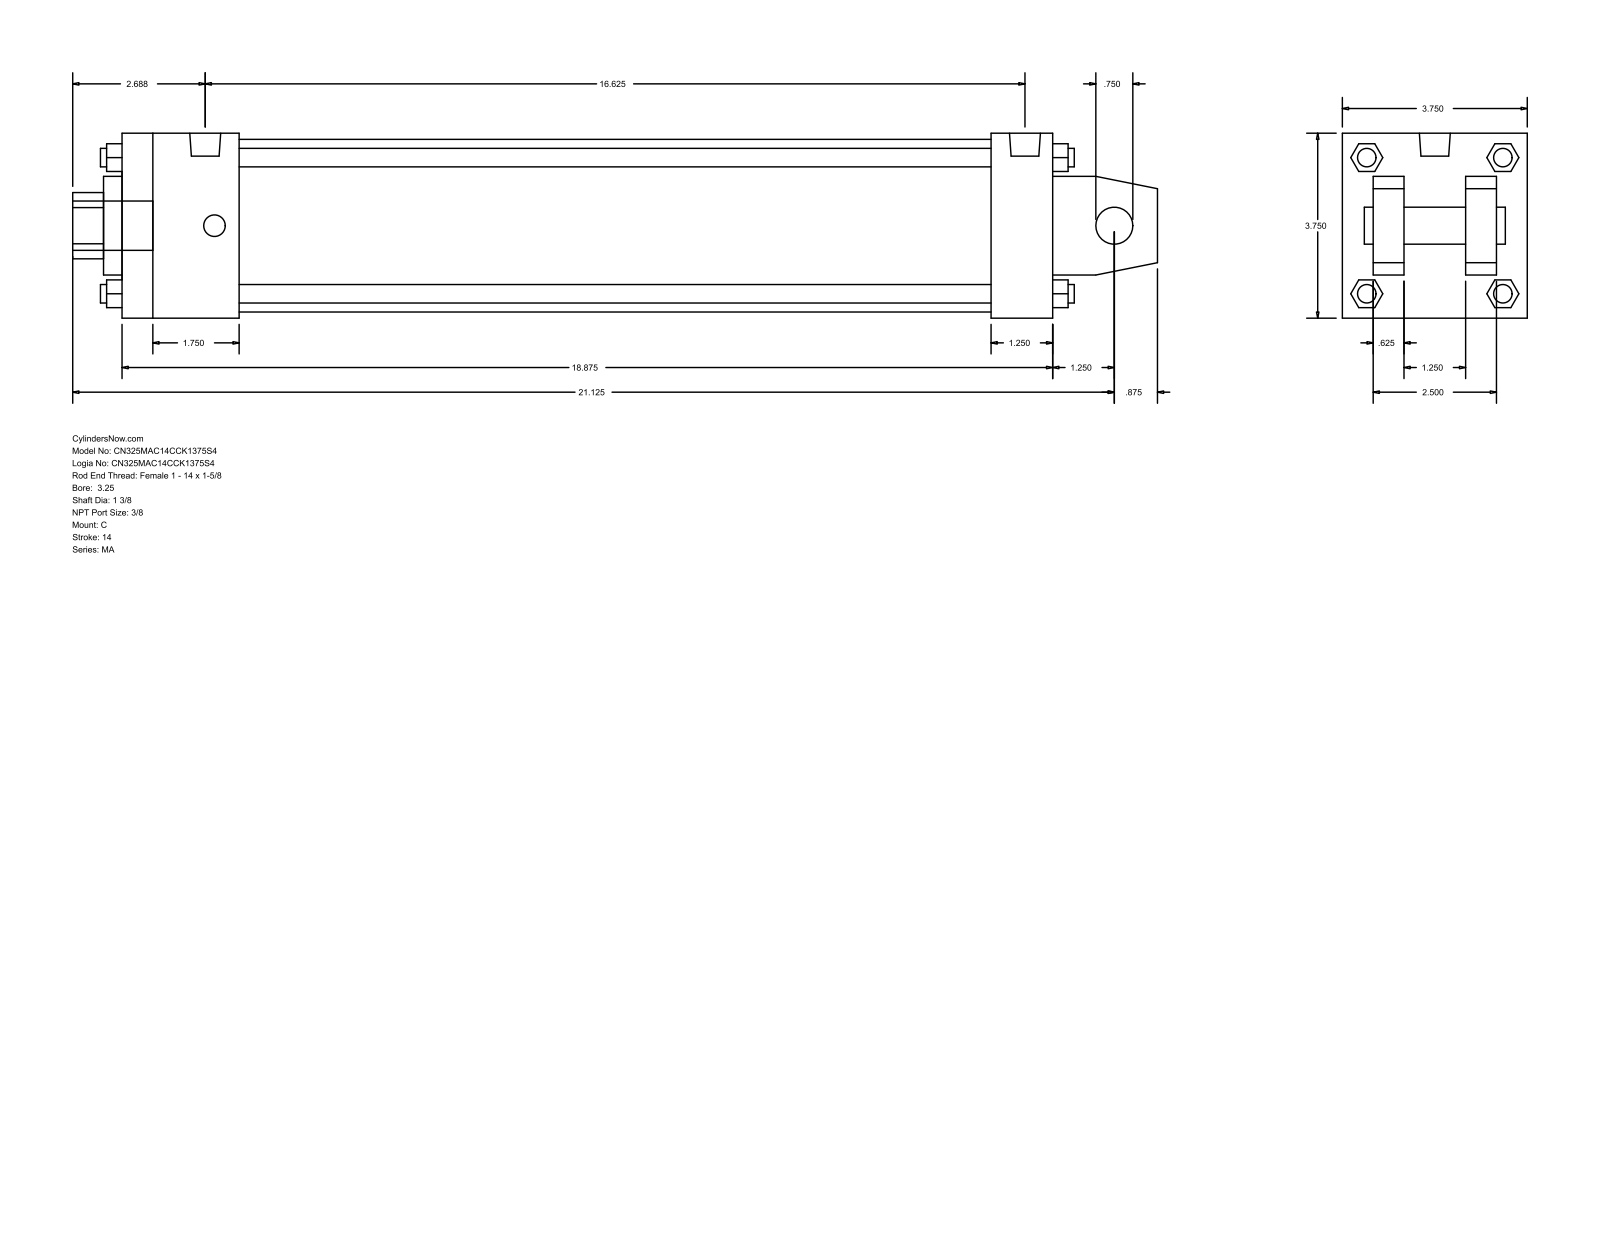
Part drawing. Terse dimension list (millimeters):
name: MA_C__0325_1.375
written by: GSSL Pune (CONFIG_CONTROL_DESIGN)
unit: mm
bodies: 0 solids, 139 faces (108 planar, 31 cylindrical, 0 other)
size: 558.8 × 95.25 × 95.25
holes: 1× ⌀19.05, 1× ⌀34.92, 1× ⌀50.8, 1× ⌀88.9
bosses: 4× ⌀11.11, 4× ⌀9.53, 2× ⌀15.93, 1× ⌀25.4
rounds: 1× R17.06
face distances: 95.24, 15.87, 63.5, 479.42, 31.74, 79.37, 47.63, 447.67, 31.75, 60.32
